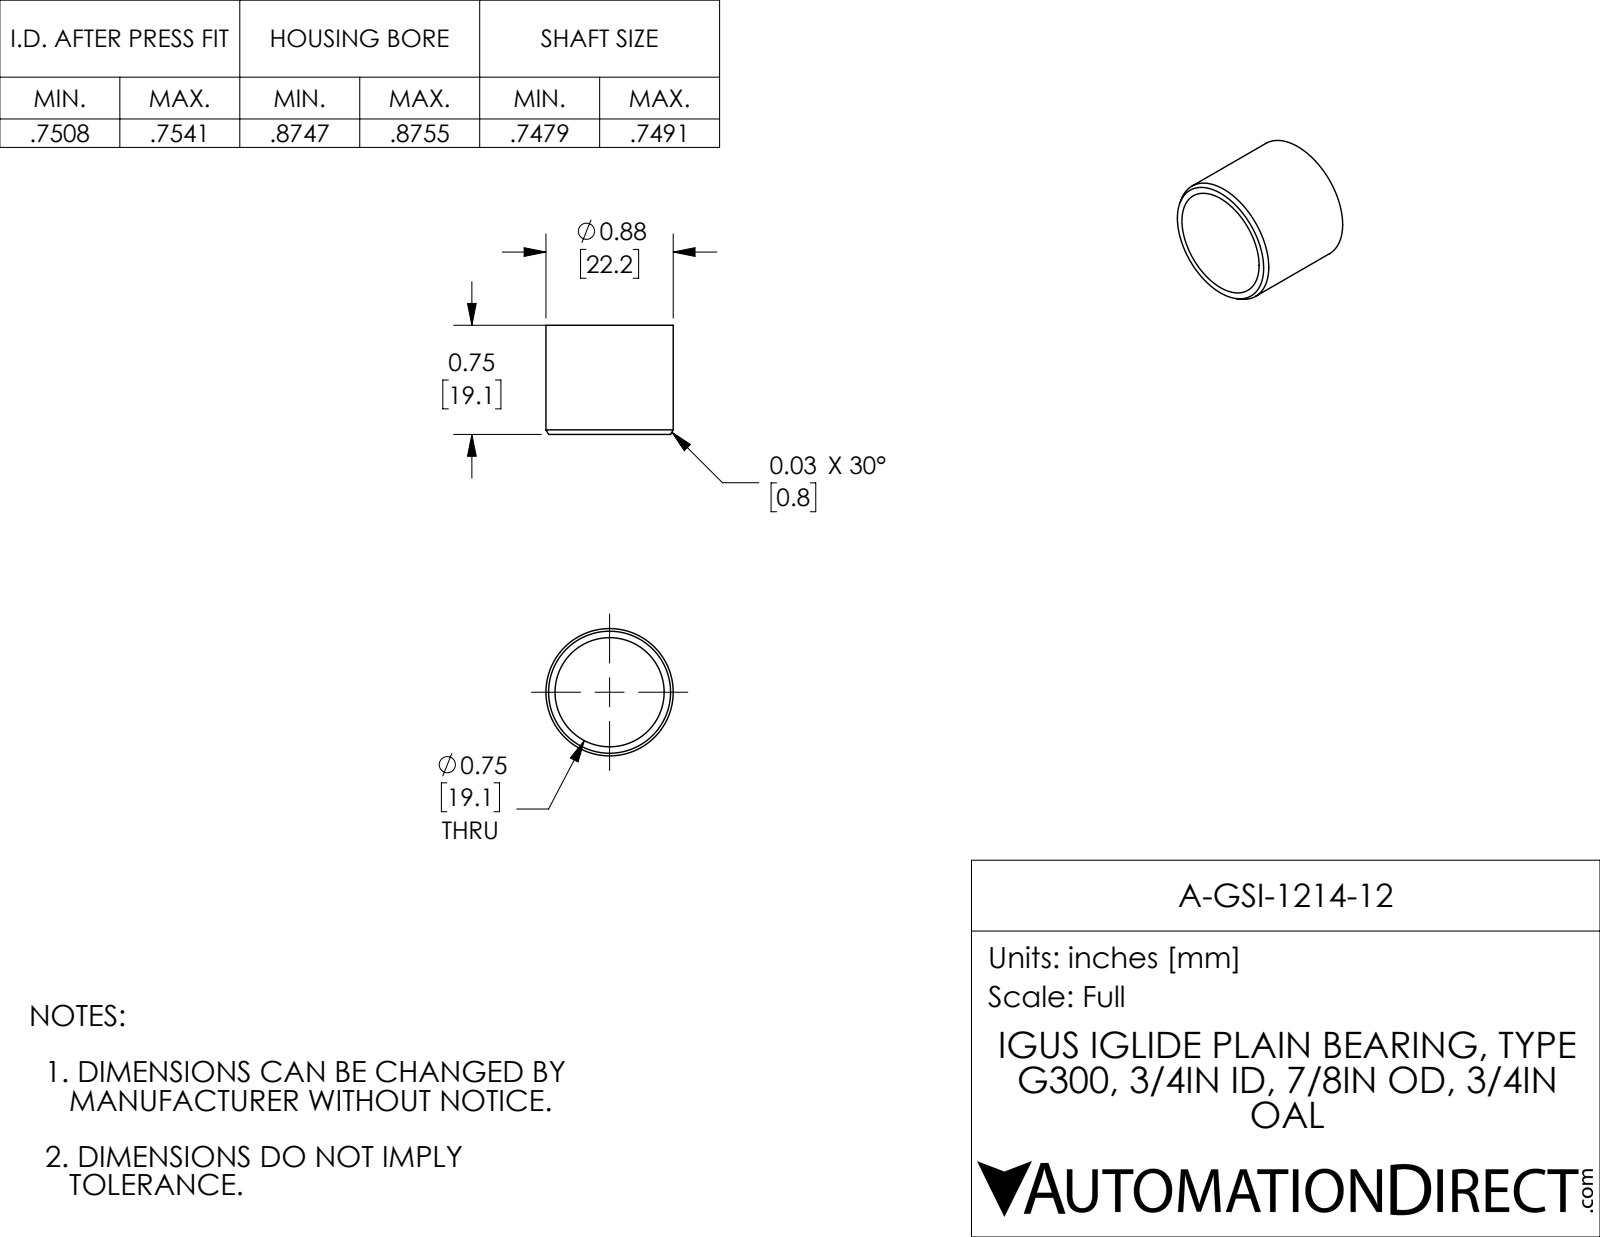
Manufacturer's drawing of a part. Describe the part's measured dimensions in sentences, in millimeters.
The part is named "A-GSI-1214-12". Its 3-D file was written by "SolidWorks 2017 (AUTOMOTIVE_DESIGN)". It is 1 solid with 10 faces: 2 planar, 4 cylindrical and 4 other. Overall it measures 22.2 by 22.2 by 19.1 millimeters. Its volume is 1 950 cubic millimeters and its surface area 2 639 square millimeters. Round holes: 1 of diameter 19.1. Round bosses or shafts: 1 of diameter 22.2. The main face-to-face distances are 19.1.
